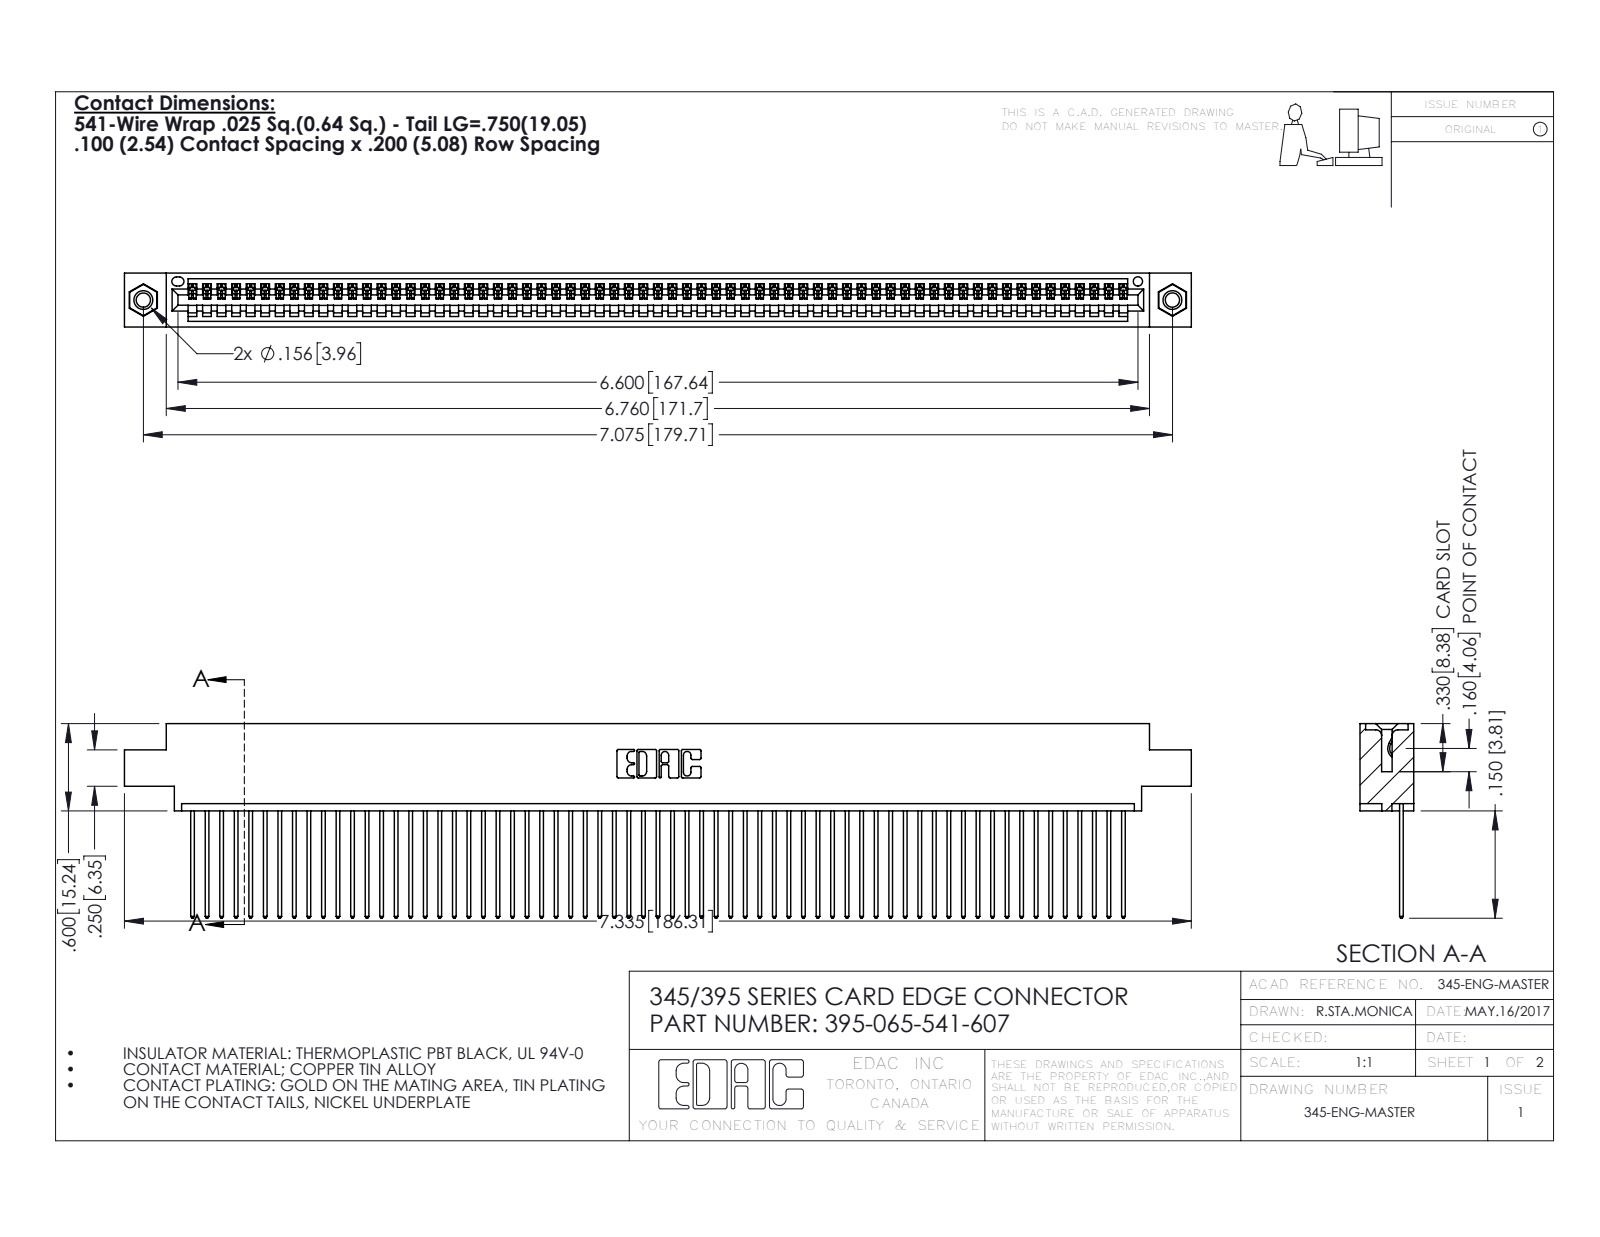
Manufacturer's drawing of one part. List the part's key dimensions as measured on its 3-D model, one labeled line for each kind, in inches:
Part name (STEP PRODUCT): 395-065-541-607; 345 Part_0.170 Offset - 0.156 Dia-TI; 345-292-001_345-293-141; 345-250-001_345-250-005-103
STEP written by: SolidWorks 2016 (CONFIG_CONTROL_DESIGN)
Units: inches
Bodies: 68 solids, 3960 faces (2716 planar, 1228 cylindrical, 16 other)
Overall size (bounding box): 7.335 × 1.337 × 0.37
Volume: 1.097 in³ · Surface area: 39.71 in²
Round holes (diameter × count): ⌀0.098 ×2, ⌀0.125 ×2, ⌀0.156 ×2, ⌀0.064 ×1
Round bosses / shafts (diameter × count): ⌀0.155 ×2
Partial cylindrical surfaces — rounded edges, fillets, slot ends (radius × count): R0.006 ×130, R0.01 ×130, R0.01 ×22, R0.007 ×6, R0.031 ×6, R0.026 ×3, R0.031 ×2, R0.04 ×2
Main face-to-face distances: 0.072, 0.298, 0.098, 0.272, 0.025, 0.37, 0.2, 0.225, 0.175, 0.149
Hole centre spacings: 0.27, 6.839, 7.075
